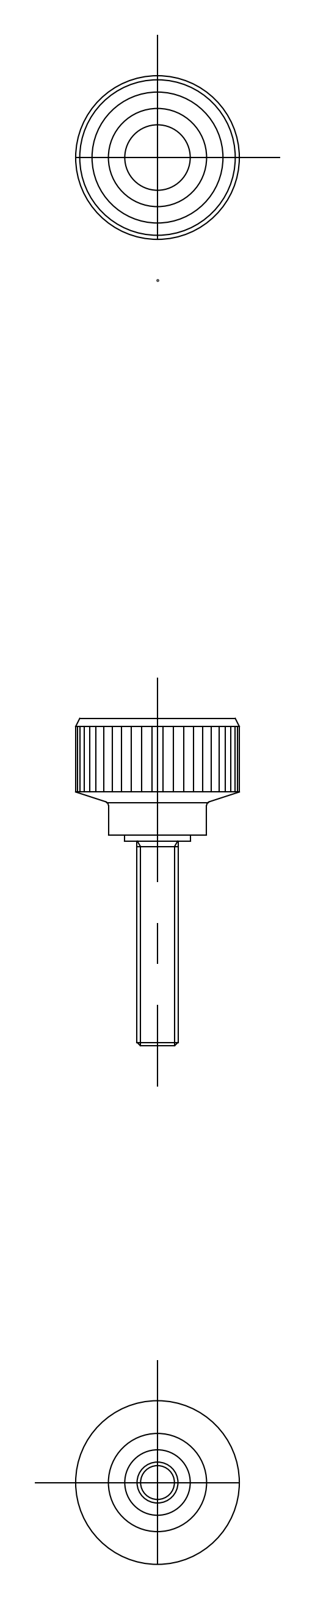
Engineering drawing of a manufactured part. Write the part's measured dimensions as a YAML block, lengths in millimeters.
part_name: "screw; knob; KKM_20_M5_25_5090_36"
step_written_by: "CADfix (AUTOMOTIVE_DESIGN)"
units: millimeters
bodies: {solids: 2, faces: 35, planar: 0, cylindrical: 0, other: 35}
overall_size: [40, 20, 20]
volume: 3237
surface_area: 2325
